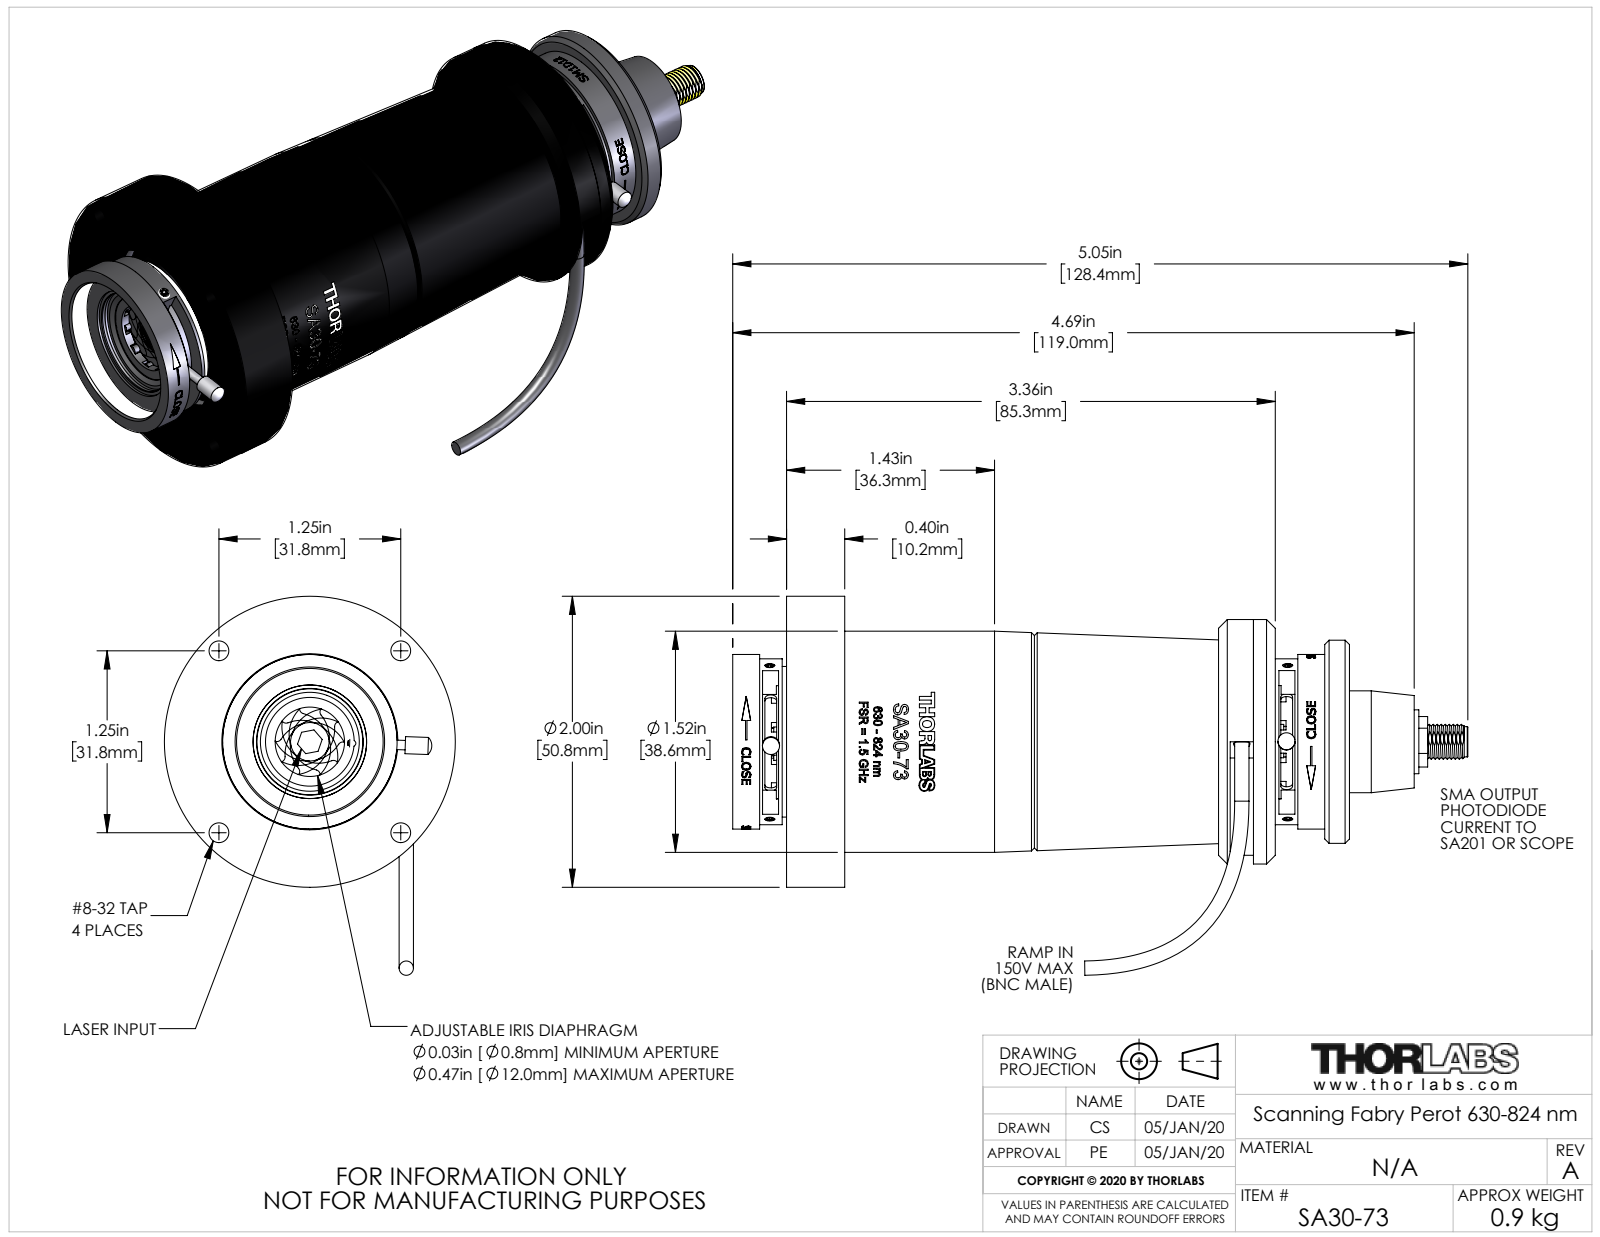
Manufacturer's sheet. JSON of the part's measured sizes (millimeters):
{"part_name": "STN052138-E0W", "step_written_by": "SolidWorks 2018 (AUTOMOTIVE_DESIGN)", "units": "millimeters", "bodies": {"solids": 42, "faces": 1576, "planar": 619, "cylindrical": 531, "other": 426}, "overall_size": [128.37, 66.16, 50.8], "volume_mm3": 54584, "surface_area_mm2": 46000, "round_holes": [[1.68, 20], [3.45, 4], [1.1, 2], [1.6, 2], [1, 1], [2.87, 1], [4.6, 1], [6.35, 1], [8.26, 1], [9.78, 1], [10.16, 1], [12.04, 1]], "round_bosses_or_shafts": [[1.52, 20], [1.65, 14], [1.65, 8], [2.18, 4], [2.98, 2], [1.63, 2], [50.8, 1], [42.67, 1]], "partial_cylinders_radius": [[0.83, 20], [0.85, 20], [1.61, 20], [6.38, 20], [9.6, 20], [0.62, 2], [3.3, 2], [25.4, 2]], "face_to_face_distances": [81.53, 3.81, 86.81, 12.96, 85.72, 1.14, 1.09, 85.67, 10.16, 71.37], "hole_center_spacings": [8.72, 12, 4.58, 14.83, 4.86, 7.41, 7.42, 14.1]}
